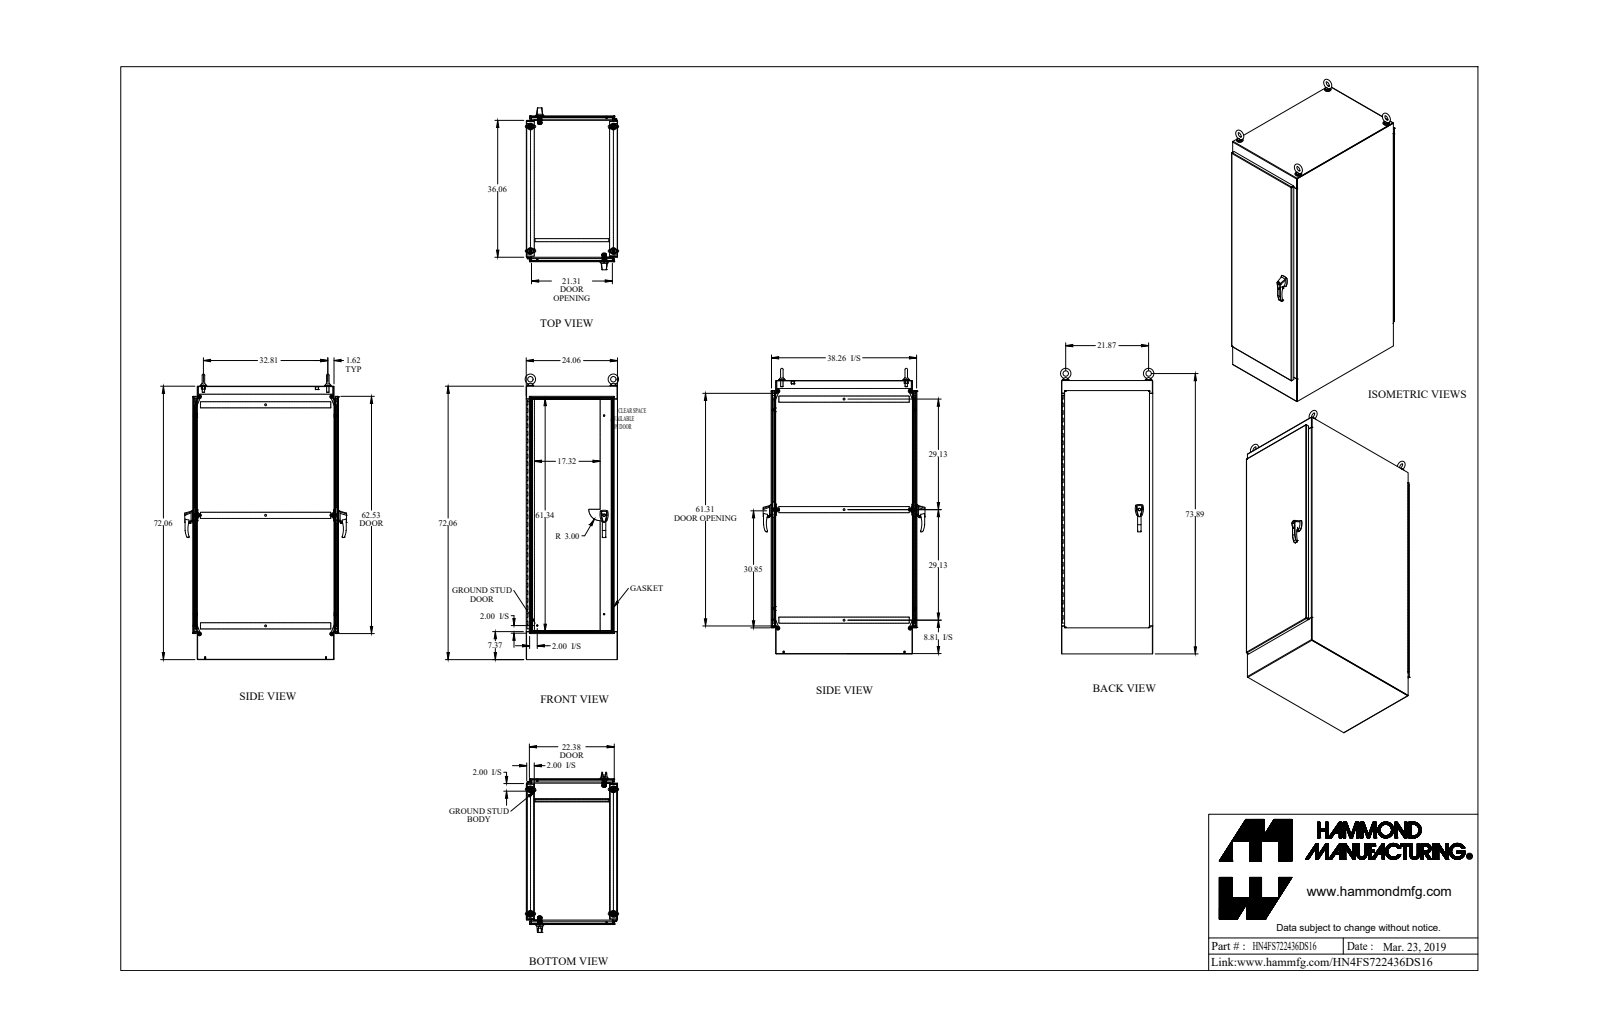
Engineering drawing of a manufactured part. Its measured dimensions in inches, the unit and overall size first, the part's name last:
Units: inches
Overall size (bounding box): 75.256 × 42.664 × 24.604
Round holes (diameter × count): ⌀0.304 ×20, ⌀0.35 ×8, ⌀0.25 ×4, ⌀0.257 ×4, ⌀0.28 ×4, ⌀0.281 ×4, ⌀0.313 ×4, ⌀0.39 ×4, ⌀0.413 ×4, ⌀0.625 ×4, ⌀0.68 ×4, ⌀0.75 ×4
Round bosses / shafts (diameter × count): ⌀1.75 ×4, ⌀1.5 ×4, ⌀1.25 ×4, ⌀1 ×4, ⌀0.75 ×4, ⌀0.738 ×4, ⌀0.63 ×4, ⌀0.44 ×4
Partial cylindrical surfaces — rounded edges, fillets, slot ends (radius × count): R0.125 ×44, R0.043 ×42, R0.138 ×36, R0.017 ×32, R0.048 ×26, R0.143 ×26, R0.5 ×26, R0.06 ×21
Main face-to-face distances: 0.095, 23.965, 23.87, 38.339, 24.06, 71.965, 1.187, 37.152, 38.244, 38.434
Hole centre spacings: 6, 23.099, 12, 25.329, 18, 28.663, 24, 32.765
Volume: 1 302 in³ · Surface area: 27 250 in²
Bodies: 94 solids, 3304 faces (1445 planar, 1531 cylindrical, 328 other)
Part name (STEP PRODUCT): HN4FS722436DS16
STEP written by: SolidWorks 2018 (AUTOMOTIVE_DESIGN)
